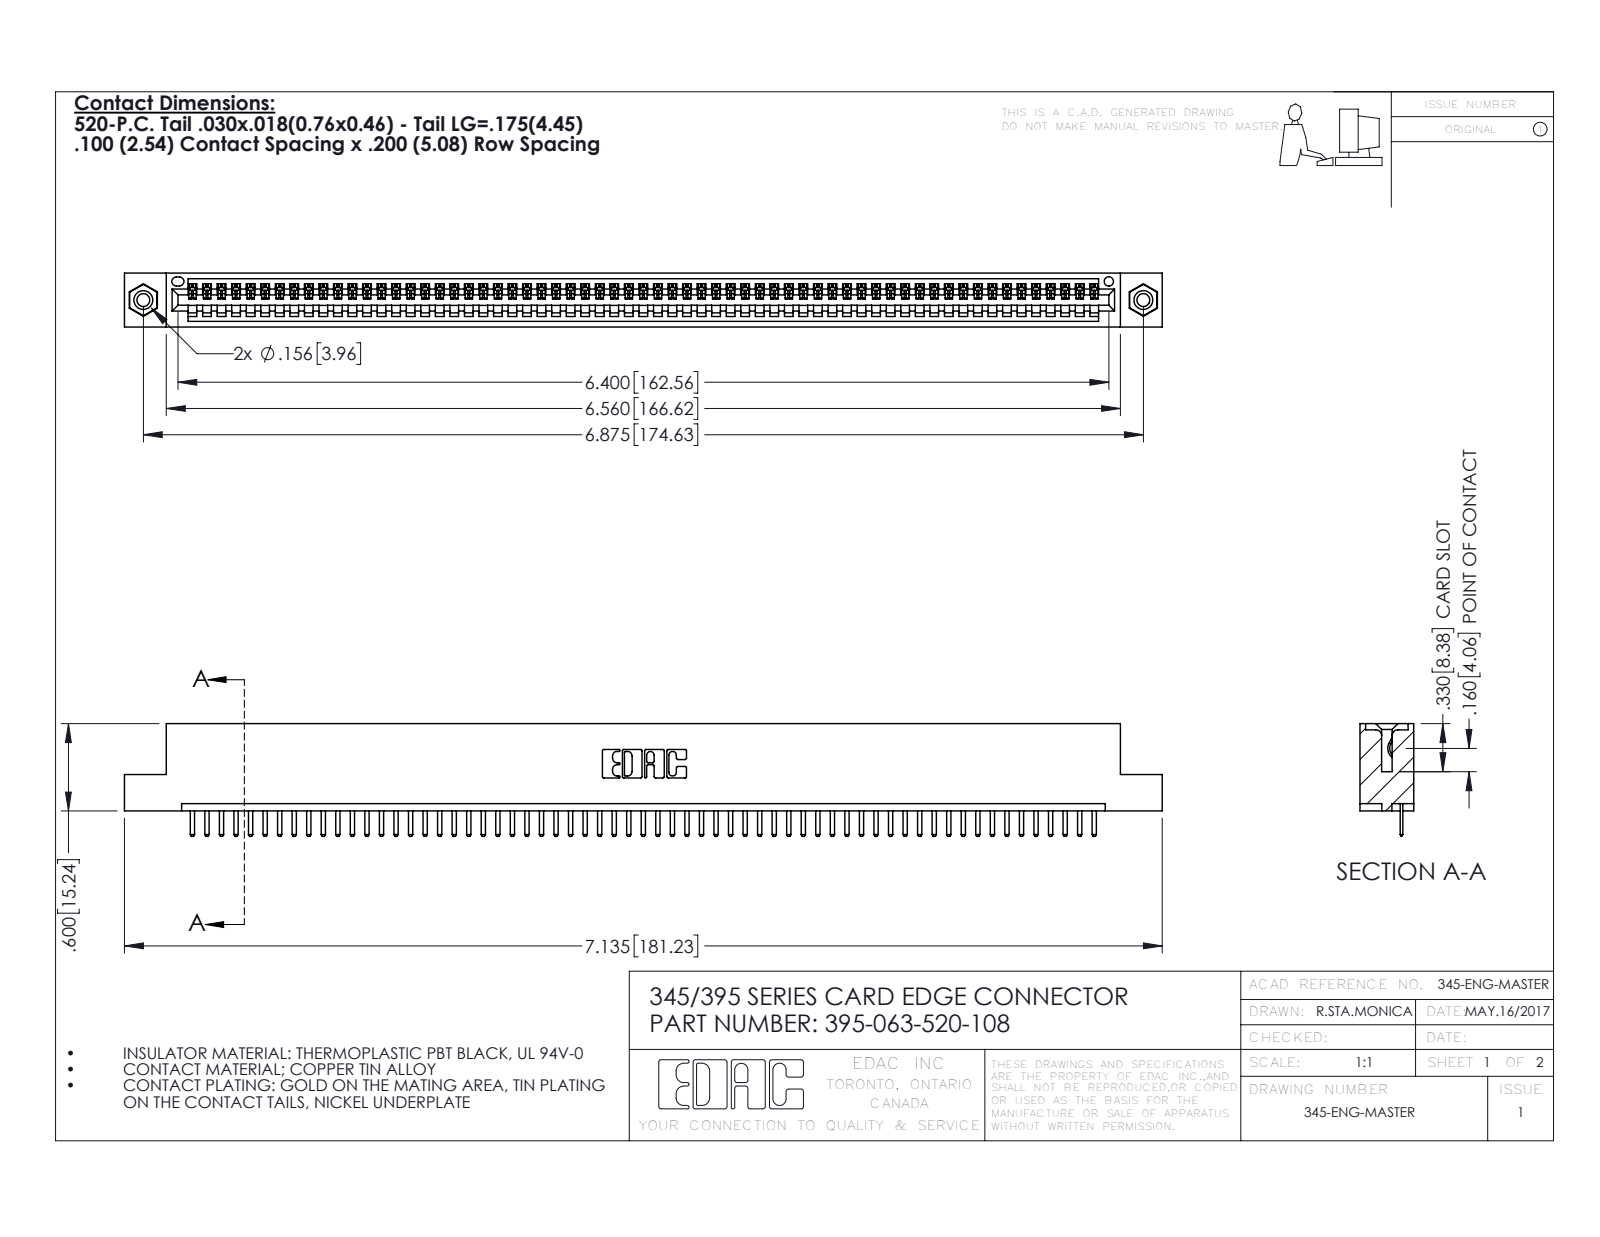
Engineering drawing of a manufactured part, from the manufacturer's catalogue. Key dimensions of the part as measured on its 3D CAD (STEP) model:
Part name (STEP PRODUCT): 345-250-001_345-250-003-102; 345 Part_Flush Mounting Lugs - 0.156 Dia-TI; 395-063-520-108; 345-292-001_345-293-120
STEP written by: SolidWorks 2016 (CONFIG_CONTROL_DESIGN)
Units: inches
Bodies: 66 solids, 4092 faces (2758 planar, 1318 cylindrical, 16 other)
Overall size (bounding box): 7.135 × 0.775 × 0.37
Volume: 1.049 in³ · Surface area: 34.98 in²
Round holes (diameter × count): ⌀0.089 ×2, ⌀0.125 ×2, ⌀0.156 ×2, ⌀0.064 ×1
Round bosses / shafts (diameter × count): ⌀0.155 ×2
Partial cylindrical surfaces — rounded edges, fillets, slot ends (radius × count): R0.01 ×128, R0.006 ×126, R0.01 ×22, R0.007 ×6, R0.031 ×6, R0.026 ×3, R0.031 ×2, R0.04 ×2
Main face-to-face distances: 0.072, 0.298, 0.37, 0.2, 0.098, 0.272, 0.025, 0.225, 0.072, 0.149
Hole centre spacings: 0.27, 6.639, 6.875
